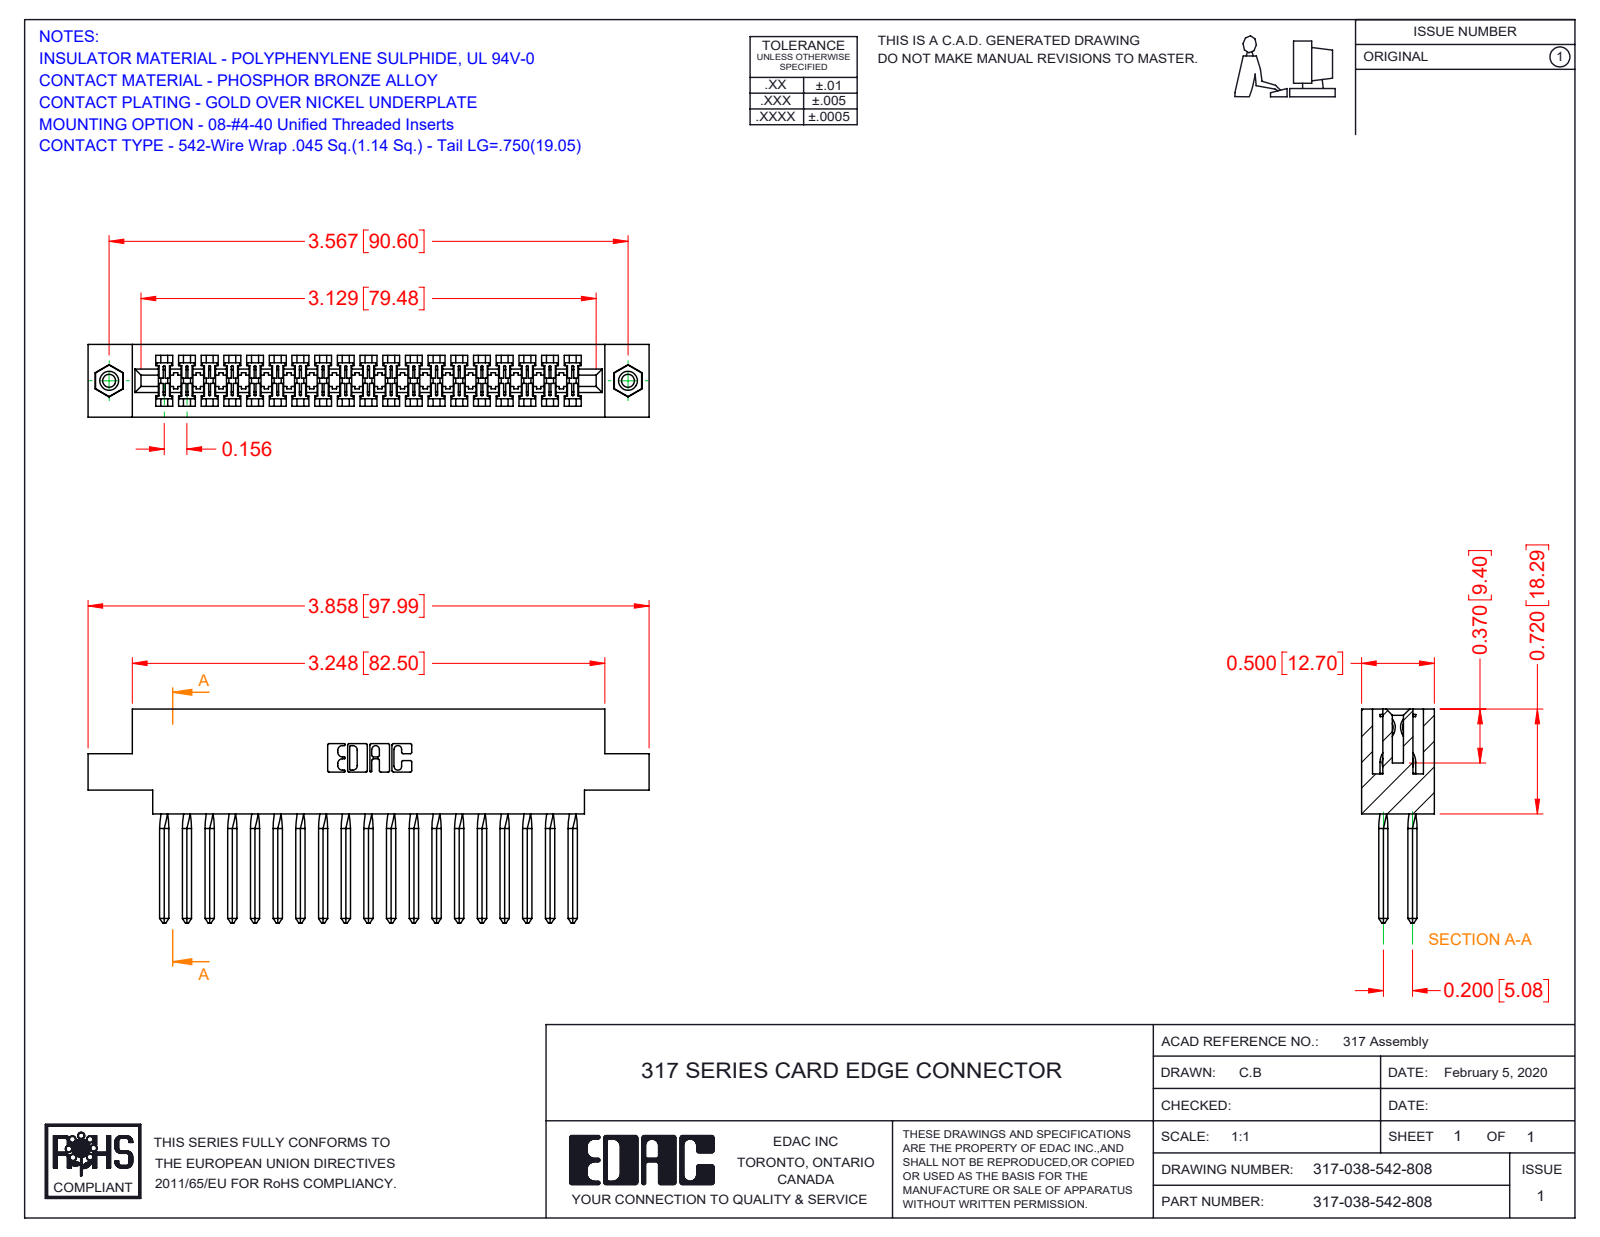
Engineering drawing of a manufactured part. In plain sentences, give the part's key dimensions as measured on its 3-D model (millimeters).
The part is named "317-038-542-878; 317-290-003_542; 345-250-001_345-250-003-102; 317 Part_.156 Dia - TI". Its 3-D file was written by "SolidWorks 2016 (CONFIG_CONTROL_DESIGN)". It is 41 solids with 2328 faces: 1838 planar, 322 cylindrical and 168 other. Overall it measures 98 by 37.3 by 12.7 millimeters. Its volume is 15 300 cubic millimeters and its surface area 20 580 square millimeters. Round holes: 2 of diameter 2.3, 2 of diameter 3.2, 2 of diameter 4. Round bosses or shafts: 2 of diameter 3.9. Partial cylindrical surfaces (rounded edges, fillets, slot ends): 76 of radius 0.2, 22 of radius 0.3, 6 of radius 0.2, 6 of radius 0.8, 3 of radius 0.7, 2 of radius 1.9, 2 of radius 2.3, 2 of radius 2.5. The main face-to-face distances are 12.7, 1.9, 10.8, 2.8, 8.9, 5.1, 2.9, 3.5, 18.3, 1.2. The hole center spacings are 90.6.
